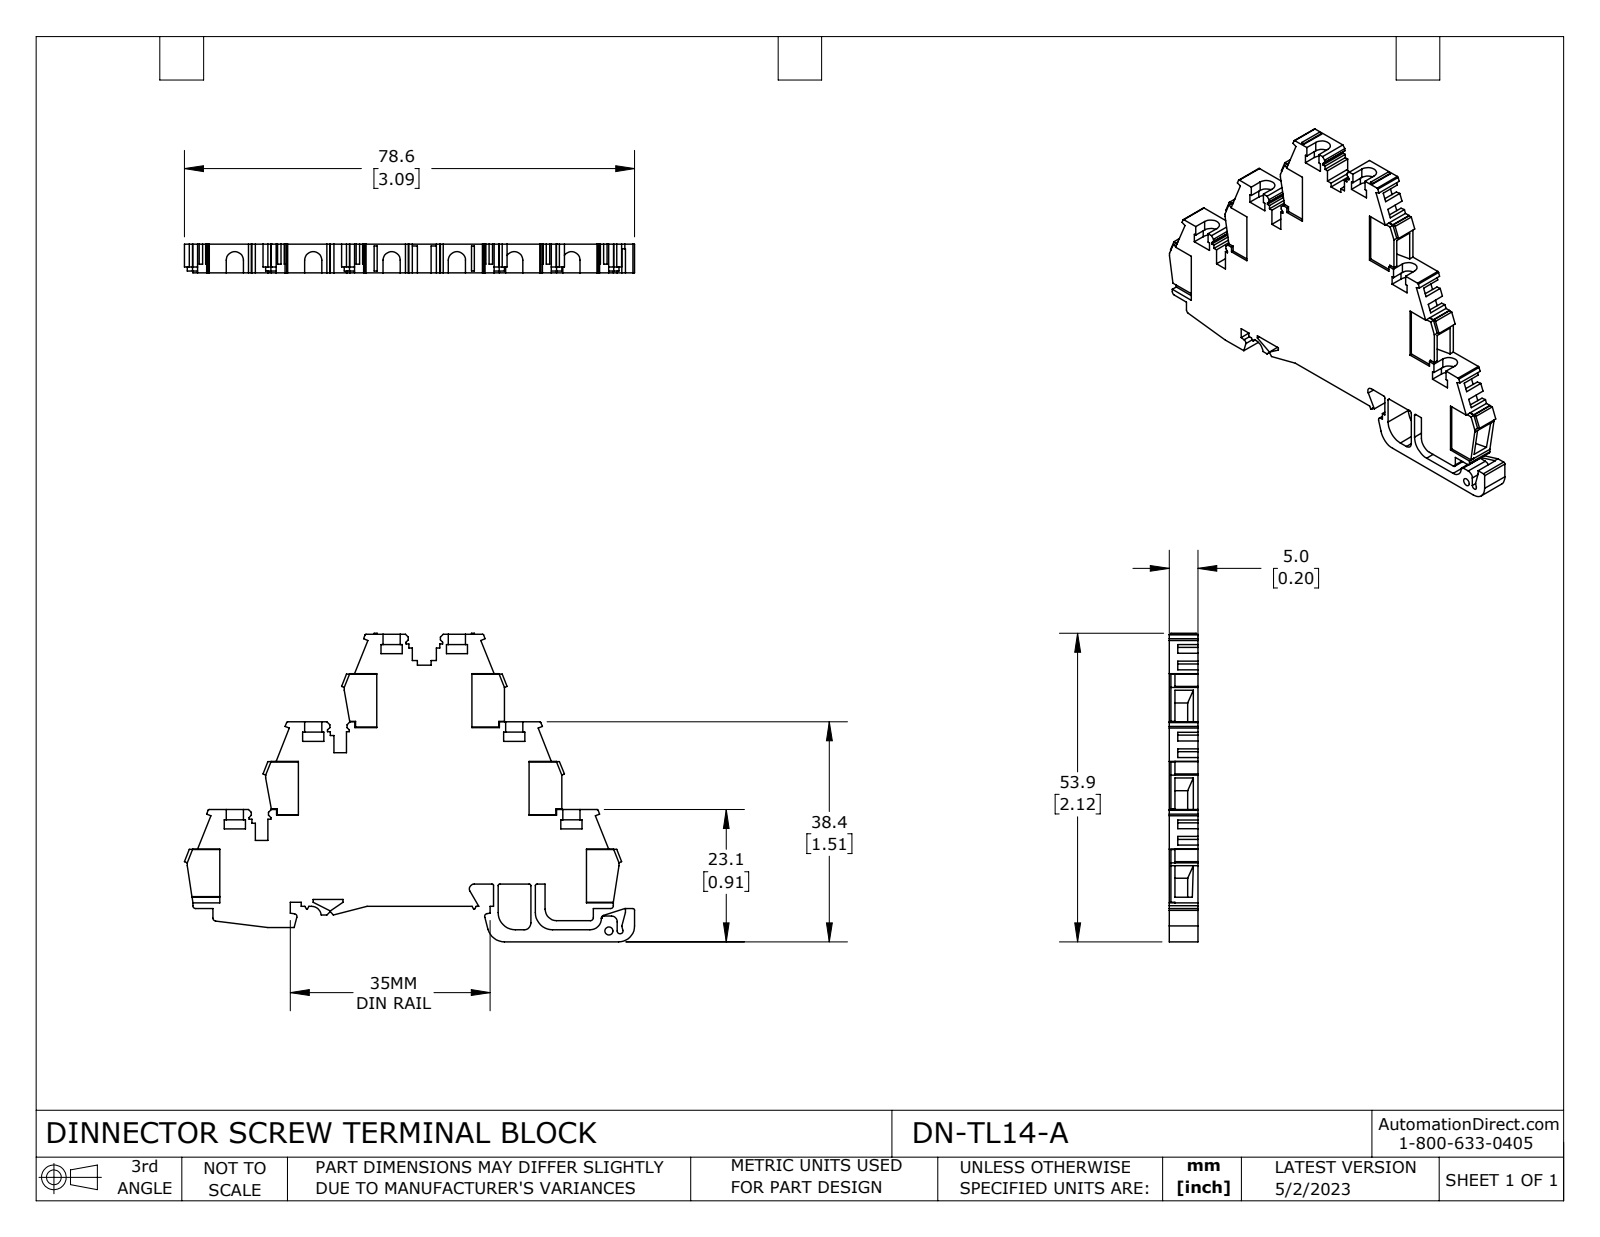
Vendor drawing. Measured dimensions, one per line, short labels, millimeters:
name: 43504_DN-TL14-A
written by: SolidWorks 2013 (AUTOMOTIVE_DESIGN)
unit: mm
bodies: 1 solid, 519 faces (453 planar, 66 cylindrical, 0 other)
size: 78.6 × 53.85 × 5
volume: 11 006 mm³; area: 8 020 mm²
holes: 6× ⌀2.6, 1× ⌀1.4
rounds: 15× R0.5, 6× R0.2, 6× R1.5, 6× R1.85, 5× R0.3, 3× R3, 2× R2, 1× R0.85
face distances: 5, 4.7, 15.3, 0.7, 1, 4, 6.2, 2.2, 3.5, 1.2
hole spacings: 18.28, 20.54, 12.05, 22.2, 29.49, 35.65, 36.56, 39.02
